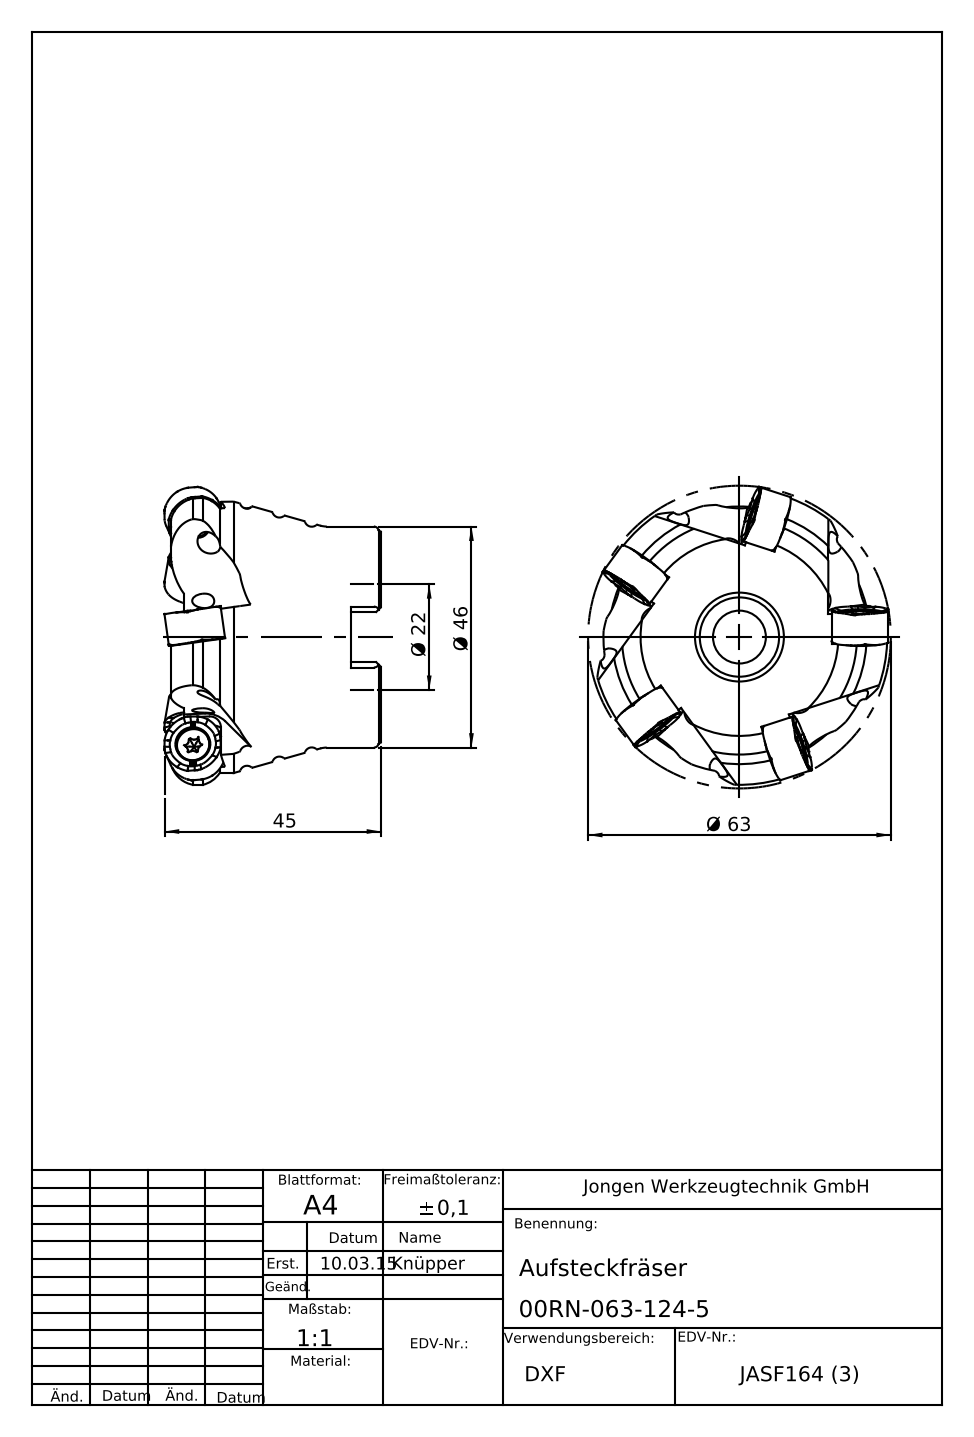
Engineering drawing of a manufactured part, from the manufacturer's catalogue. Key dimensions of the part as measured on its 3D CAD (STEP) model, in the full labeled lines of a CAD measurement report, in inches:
Part name (STEP PRODUCT): 00RN_063_124_5
STEP written by: SolidWorks 2016 (AUTOMOTIVE_DESIGN)
Units: inches
Bodies: 1 solid, 190 faces (63 planar, 55 cylindrical, 72 other)
Overall size (bounding box): 2.48 × 2.48 × 1.775
Volume: 4.729 in³ · Surface area: 26.62 in²
Round holes (diameter × count): ⌀0.118 ×5, ⌀0.433 ×1, ⌀0.65 ×1, ⌀0.866 ×1, ⌀0.872 ×1, ⌀0.878 ×1
Round bosses / shafts (diameter × count): ⌀1.811 ×1
Partial cylindrical surfaces — rounded edges, fillets, slot ends (radius × count): R0.085 ×5, R0.098 ×5, R0.177 ×5, R0.236 ×5, R1.114 ×1
Main face-to-face distances: 1.614, 0.248, 1.366, 0.866, 0.618, 0.748, 1.13, 0.882, 0.264, 0.484
